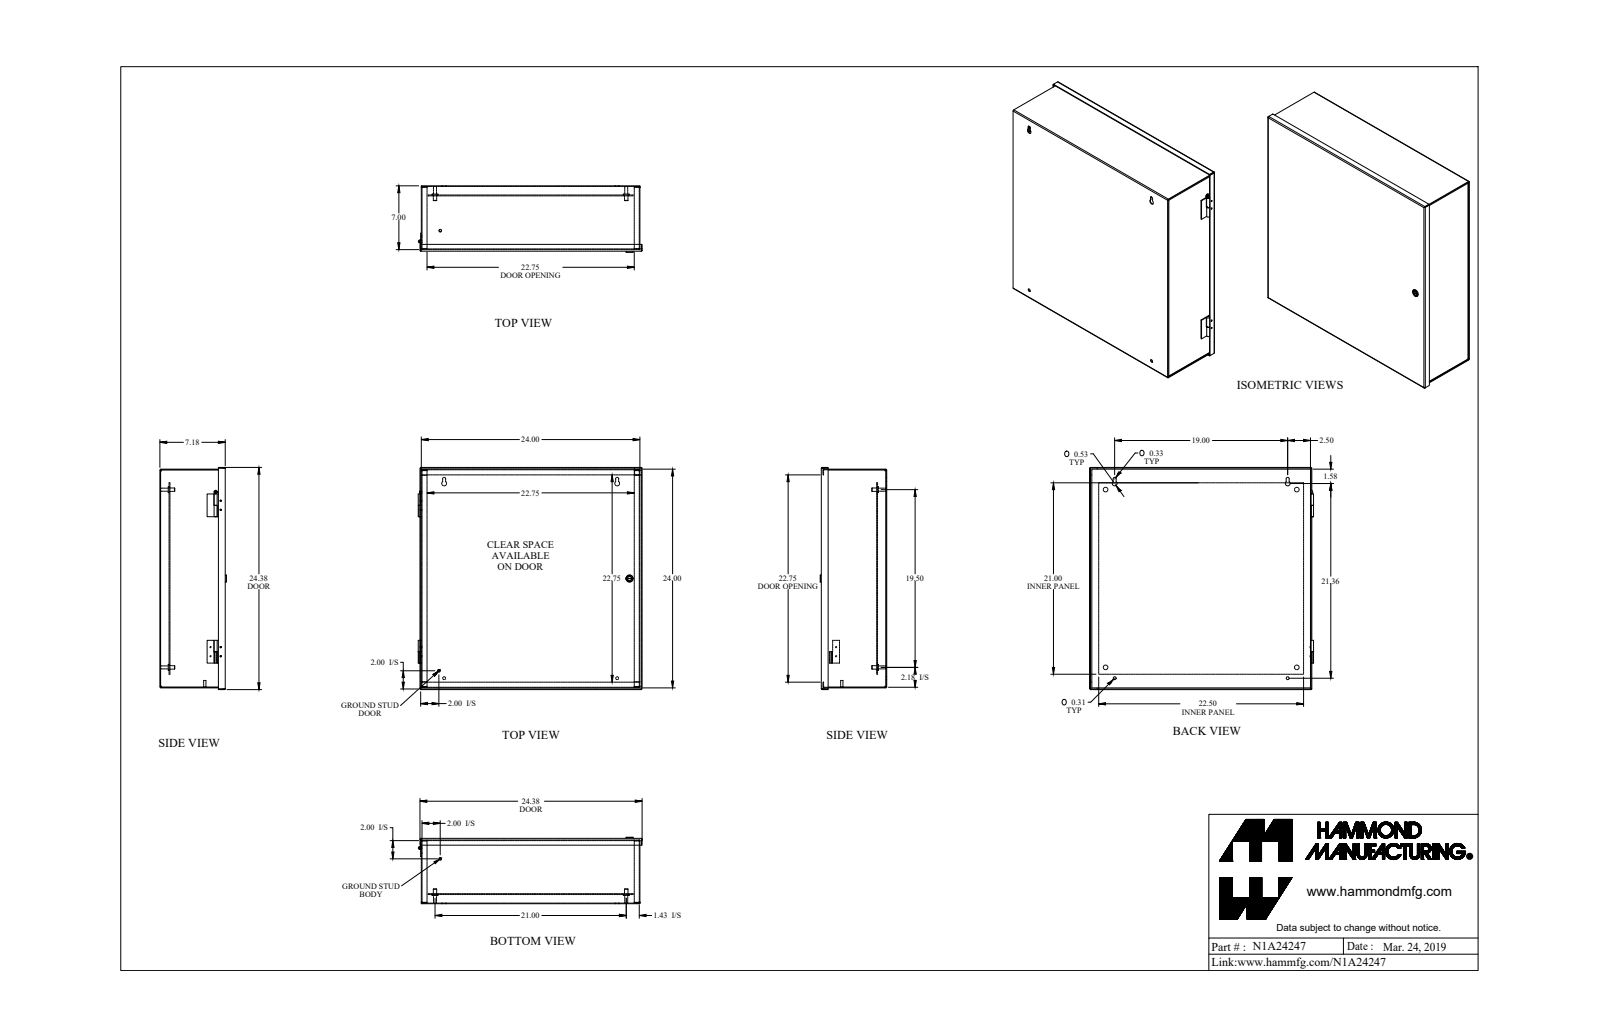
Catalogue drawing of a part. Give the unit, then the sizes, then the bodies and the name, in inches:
Units: inches
Overall size (bounding box): 24.574 × 24.384 × 7.299
Round holes (diameter × count): ⌀0.14 ×8, ⌀0.5 ×4, ⌀0.307 ×2, ⌀0.312 ×2, ⌀0.445 ×2, ⌀0.17 ×1, ⌀0.187 ×1, ⌀0.516 ×1
Round bosses / shafts (diameter × count): ⌀0.128 ×8, ⌀0.375 ×5, ⌀0.65 ×4, ⌀0.33 ×4, ⌀1 ×2, ⌀0.281 ×2, ⌀0.25 ×2, ⌀0.788 ×1
Partial cylindrical surfaces — rounded edges, fillets, slot ends (radius × count): R0.036 ×16, R0.108 ×16, R0.06 ×2, R0.153 ×2, R0.164 ×2, R0.266 ×2, R0.03 ×1, R0.125 ×1
Main face-to-face distances: 0.072, 7.105, 23.928, 7.033, 7.177, 1.104, 1.032, 6.001, 6.073, 1.009
Hole centre spacings: 1, 1.119, 1.104, 1.553, 2.031, 9.757, 16.062, 16.062
Volume: 189.9 in³ · Surface area: 4 992 in²
Bodies: 23 solids, 520 faces (294 planar, 182 cylindrical, 44 other)
Part name (STEP PRODUCT): N1A24247
STEP written by: SolidWorks 2018 (AUTOMOTIVE_DESIGN)
